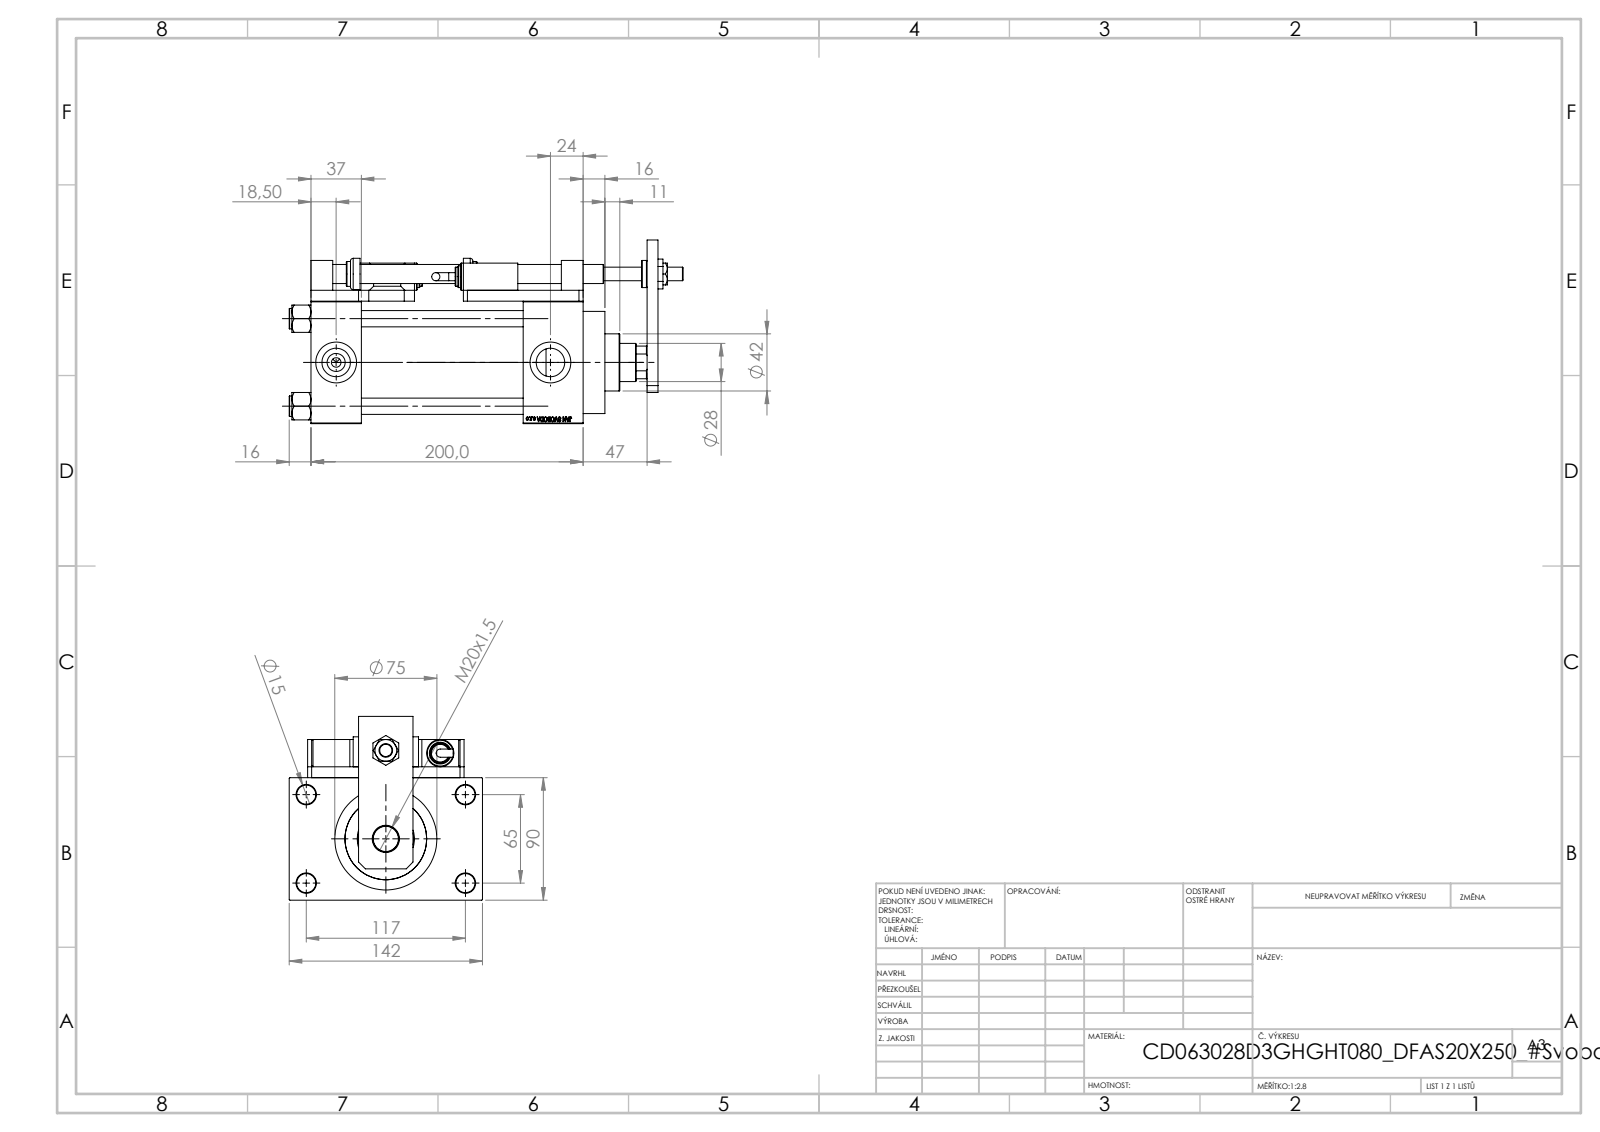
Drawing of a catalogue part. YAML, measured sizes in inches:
part_name: "V215CD_VCP_D; V215CD_D_TYCINKA; Zatka_pro_OIL_PORT; V215CD_SWITCH_Q_SWITCH (+8 more)"
step_written_by: "SolidWorks 2019 (CONFIG_CONTROL_DESIGN)"
units: inches
bodies: {solids: 26, faces: 1432, planar: 666, cylindrical: 167, other: 599}
overall_size: [11.398, 5.591, 5.315]
volume: 89.52
surface_area: 514.6
round_holes:
  - {diameter: 0.551, count: 5}
  - {diameter: 0.335, count: 4}
  - {diameter: 0.472, count: 4}
  - {diameter: 0.531, count: 4}
  - {diameter: 0.825, count: 4}
  - {diameter: 1.181, count: 4}
  - {diameter: 0.276, count: 3}
  - {diameter: 0.394, count: 1}
  - {diameter: 0.728, count: 1}
  - {diameter: 0.787, count: 1}
  - {diameter: 1.102, count: 1}
  - {diameter: 1.22, count: 1}
round_bosses_or_shafts:
  - {diameter: 0.591, count: 4}
  - {diameter: 0.787, count: 3}
  - {diameter: 0.63, count: 2}
  - {diameter: 0.551, count: 2}
  - {diameter: 0.236, count: 2}
  - {diameter: 2.953, count: 1}
  - {diameter: 2.717, count: 1}
  - {diameter: 1.654, count: 1}
partial_cylinders:
  - {radius: 0.295, count: 4}
  - {radius: 0.531, count: 1}
face_to_face_distances: [0.315, 3.543, 1.732, 7.874, 1.457, 3.858, 6.417, 6.142, 4.685, 1.85]
hole_center_spacings: [2.635, 1.037, 1.79, 2.531, 2.748, 3.569, 4.383, 2.559]
